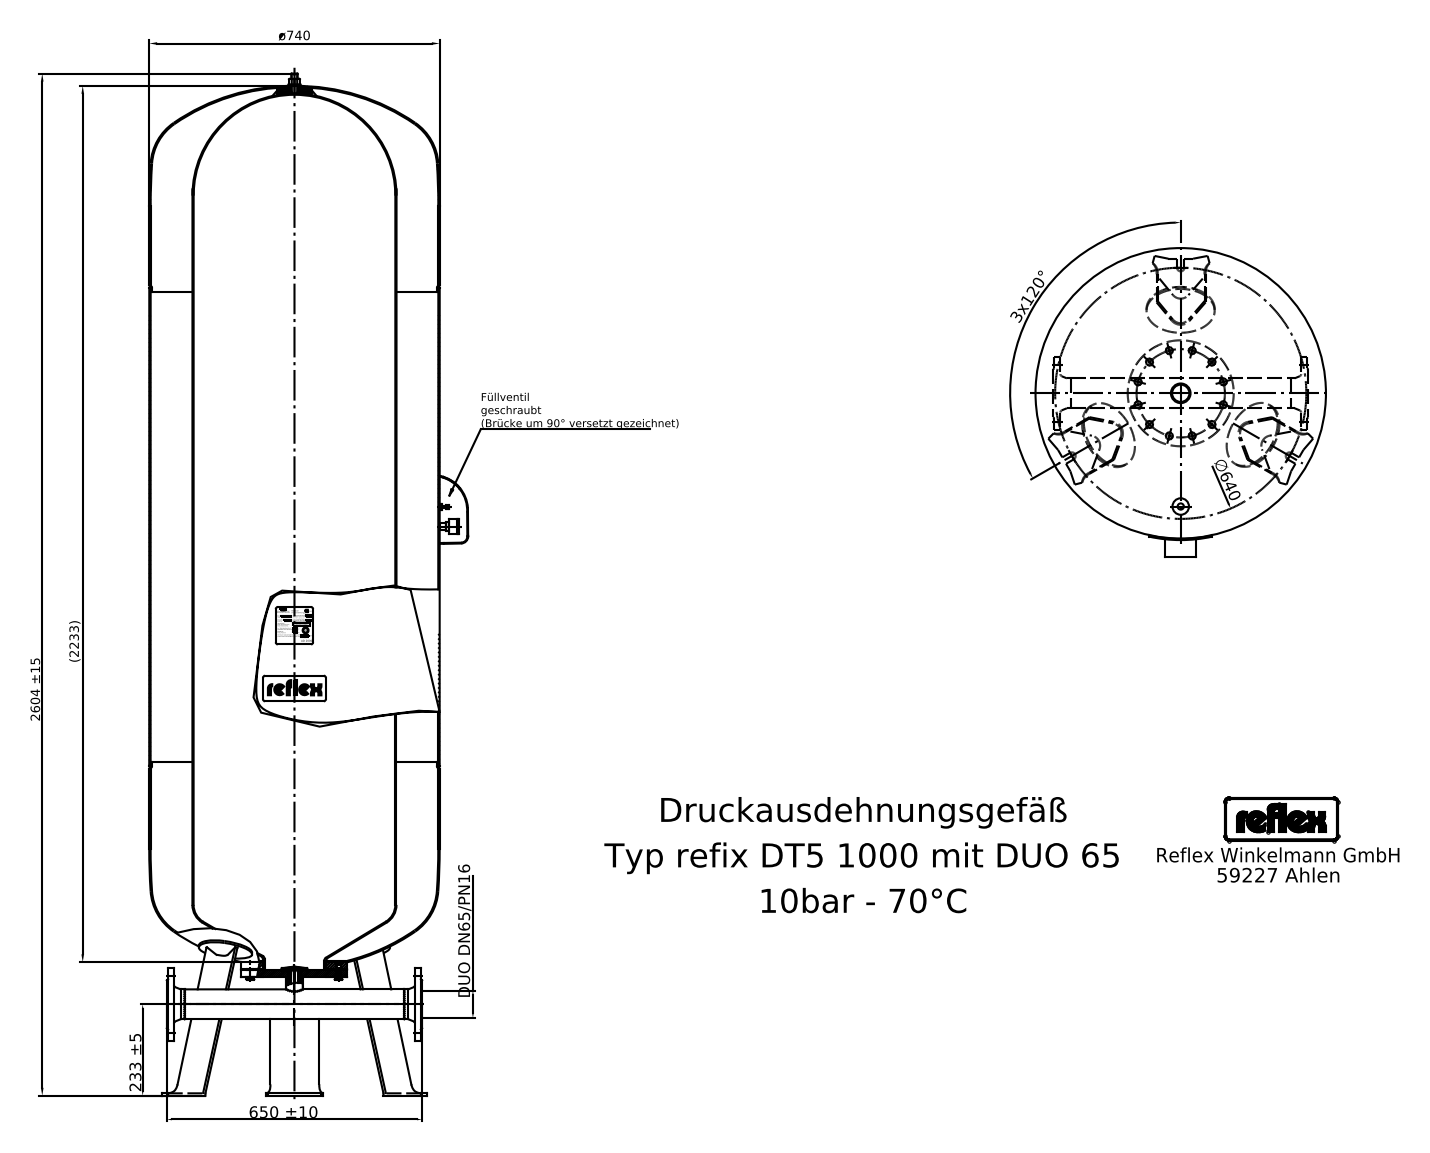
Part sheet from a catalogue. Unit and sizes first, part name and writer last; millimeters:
Units: millimetres
Overall size (bounding box): 2604 × 810.1 × 740
Round holes (diameter × count): ⌀19 ×4, ⌀2.48 ×1, ⌀3.8 ×1, ⌀4.3 ×1, ⌀4.4 ×1, ⌀5.45 ×1, ⌀7 ×1, ⌀8 ×1, ⌀11.4 ×1, ⌀76.1 ×1, ⌀157 ×1, ⌀250 ×1
Round bosses / shafts (diameter × count): ⌀10 ×9, ⌀740 ×1, ⌀260 ×1, ⌀230 ×1, ⌀185 ×1, ⌀62 ×1, ⌀42.4 ×1, ⌀34 ×1
Partial cylindrical surfaces — rounded edges, fillets, slot ends (radius × count): R25 ×18, R5.62 ×4, R2.25 ×3, R9 ×3, R3.84 ×2, R6.75 ×2, R8 ×2, R9.27 ×2
Main face-to-face distances: 1872, 6, 195, 2067, 5.97, 5.89, 201, 2073, 311, 5
Hole centre spacings: 72.51, 102.54, 145.01, 50
Volume: 918 400 000 mm³ · Surface area: 8 512 000 mm²
Bodies: 26 solids, 522 faces (233 planar, 155 cylindrical, 134 other)
STEP written by: Mechanical Desktop 2008 (CONFIG_CONTROL_DESIGN)
